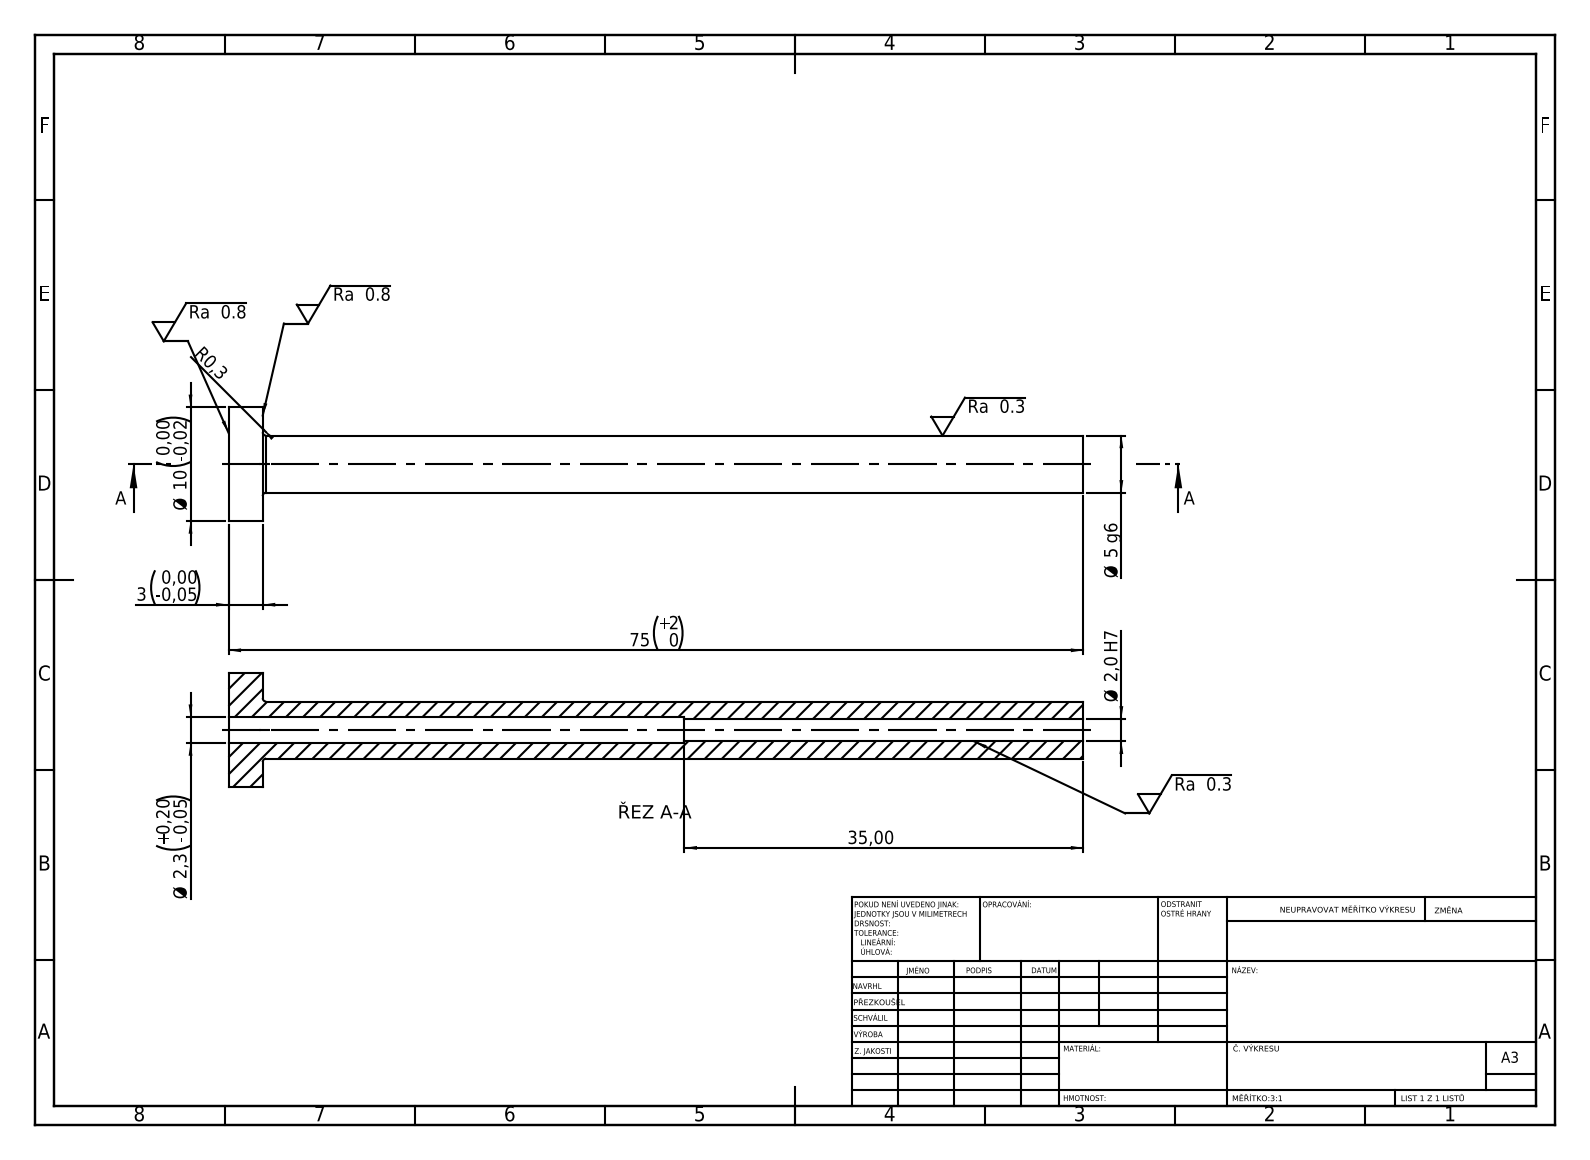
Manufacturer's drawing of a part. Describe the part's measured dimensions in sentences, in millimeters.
Its 3-D file was written by "SolidWorks 2019 (CONFIG_CONTROL_DESIGN)". It is 1 solid with 14 faces: 4 planar, 8 cylindrical and 2 other. Overall it measures 75 by 10 by 10 millimeters. Its volume is 1 374 cubic millimeters and its surface area 1 883 square millimeters. Round holes: 1 of diameter 2, 1 of diameter 2.3. Round bosses or shafts: 1 of diameter 10, 1 of diameter 5. The main face-to-face distances are 3, 75, 72, 40, 37, 35.
